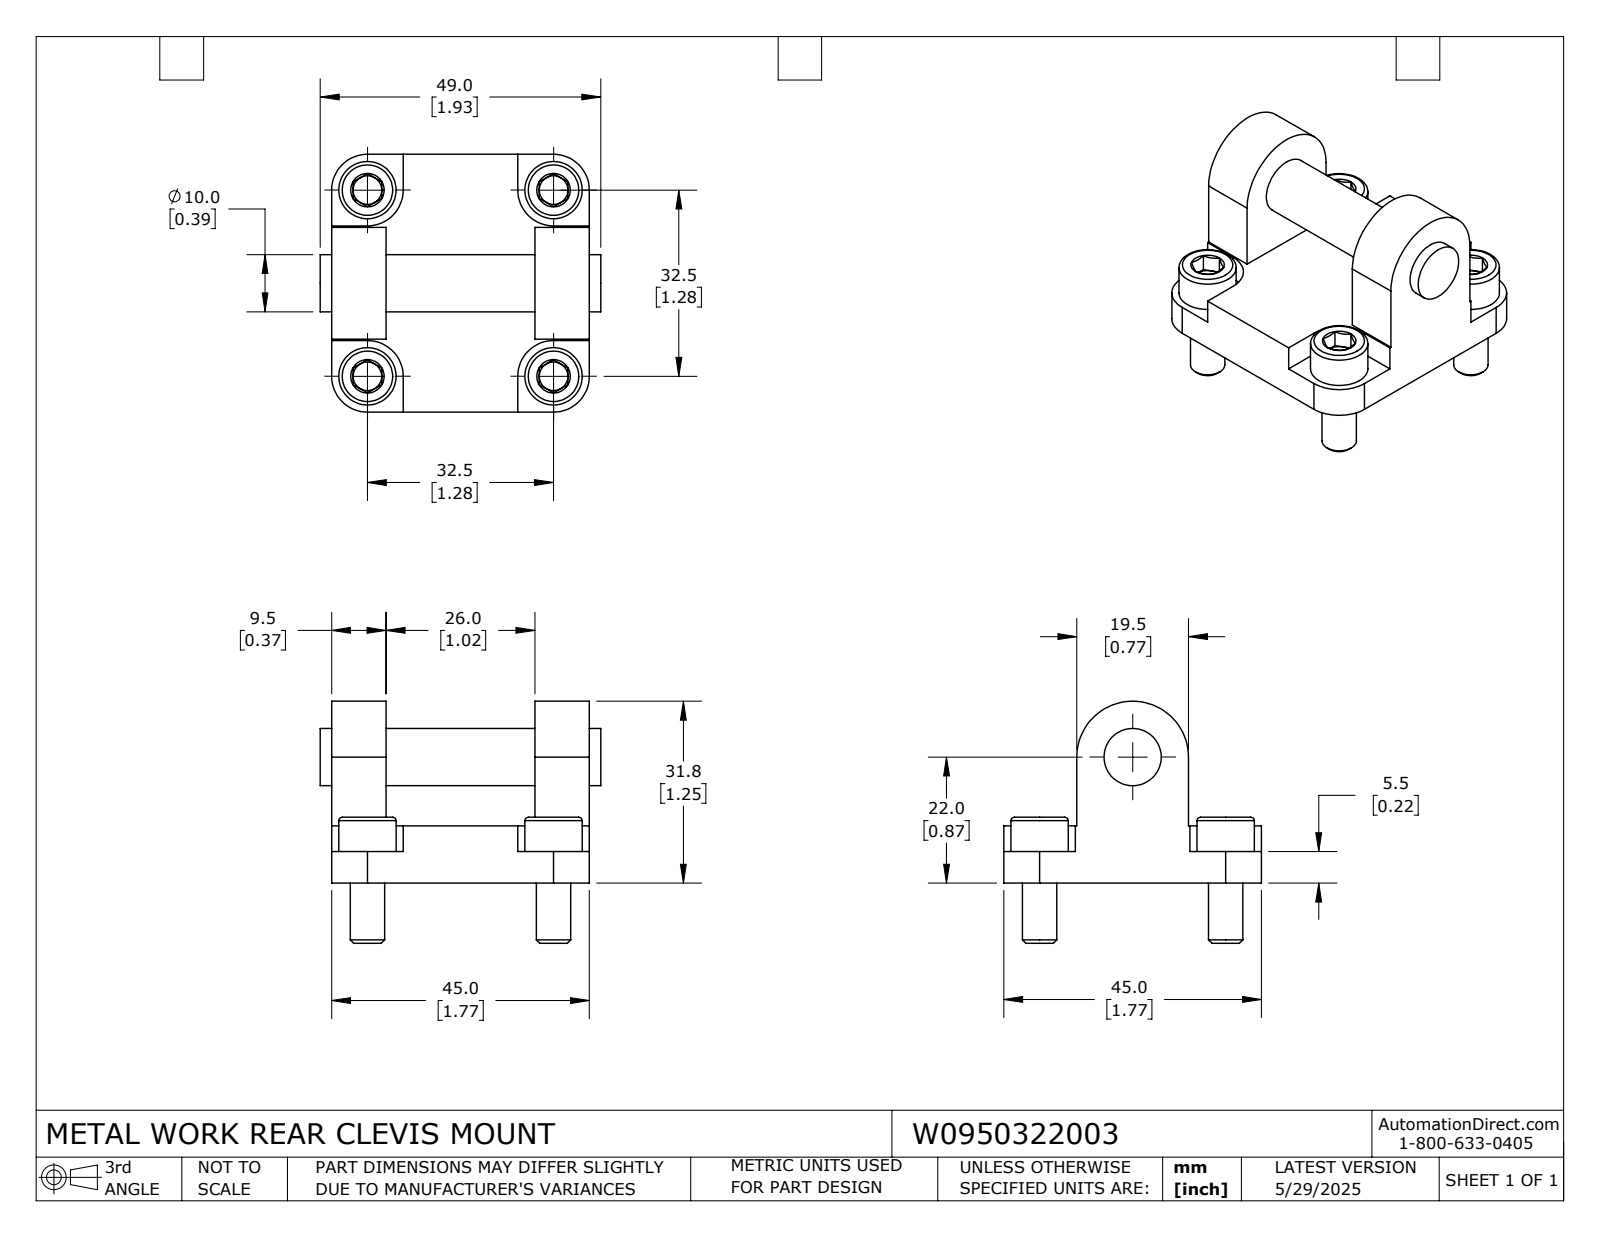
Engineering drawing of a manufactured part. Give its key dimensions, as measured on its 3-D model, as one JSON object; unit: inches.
{"part_name": "W0950322003", "step_written_by": "SolidWorks 2024 (CONFIG_CONTROL_DESIGN)", "units": "inches", "bodies": {"solids": 5, "faces": 185, "planar": 87, "cylindrical": 42, "other": 56}, "overall_size": [1.929, 1.772, 1.663], "volume_in3": 1.509, "surface_area_in2": 18.95, "round_holes": [[0.26, 4], [1.181, 1]], "round_bosses_or_shafts": [[0.394, 5], [0.236, 4]], "partial_cylinders_radius": [[0.246, 4], [0.384, 1]], "face_to_face_distances": [0.394, 1.772, 0.118, 0.059, 0.177, 0.276, 0.374, 1.398, 0.217, 0.502], "hole_center_spacings": [0.905, 1.28, 1.809]}
